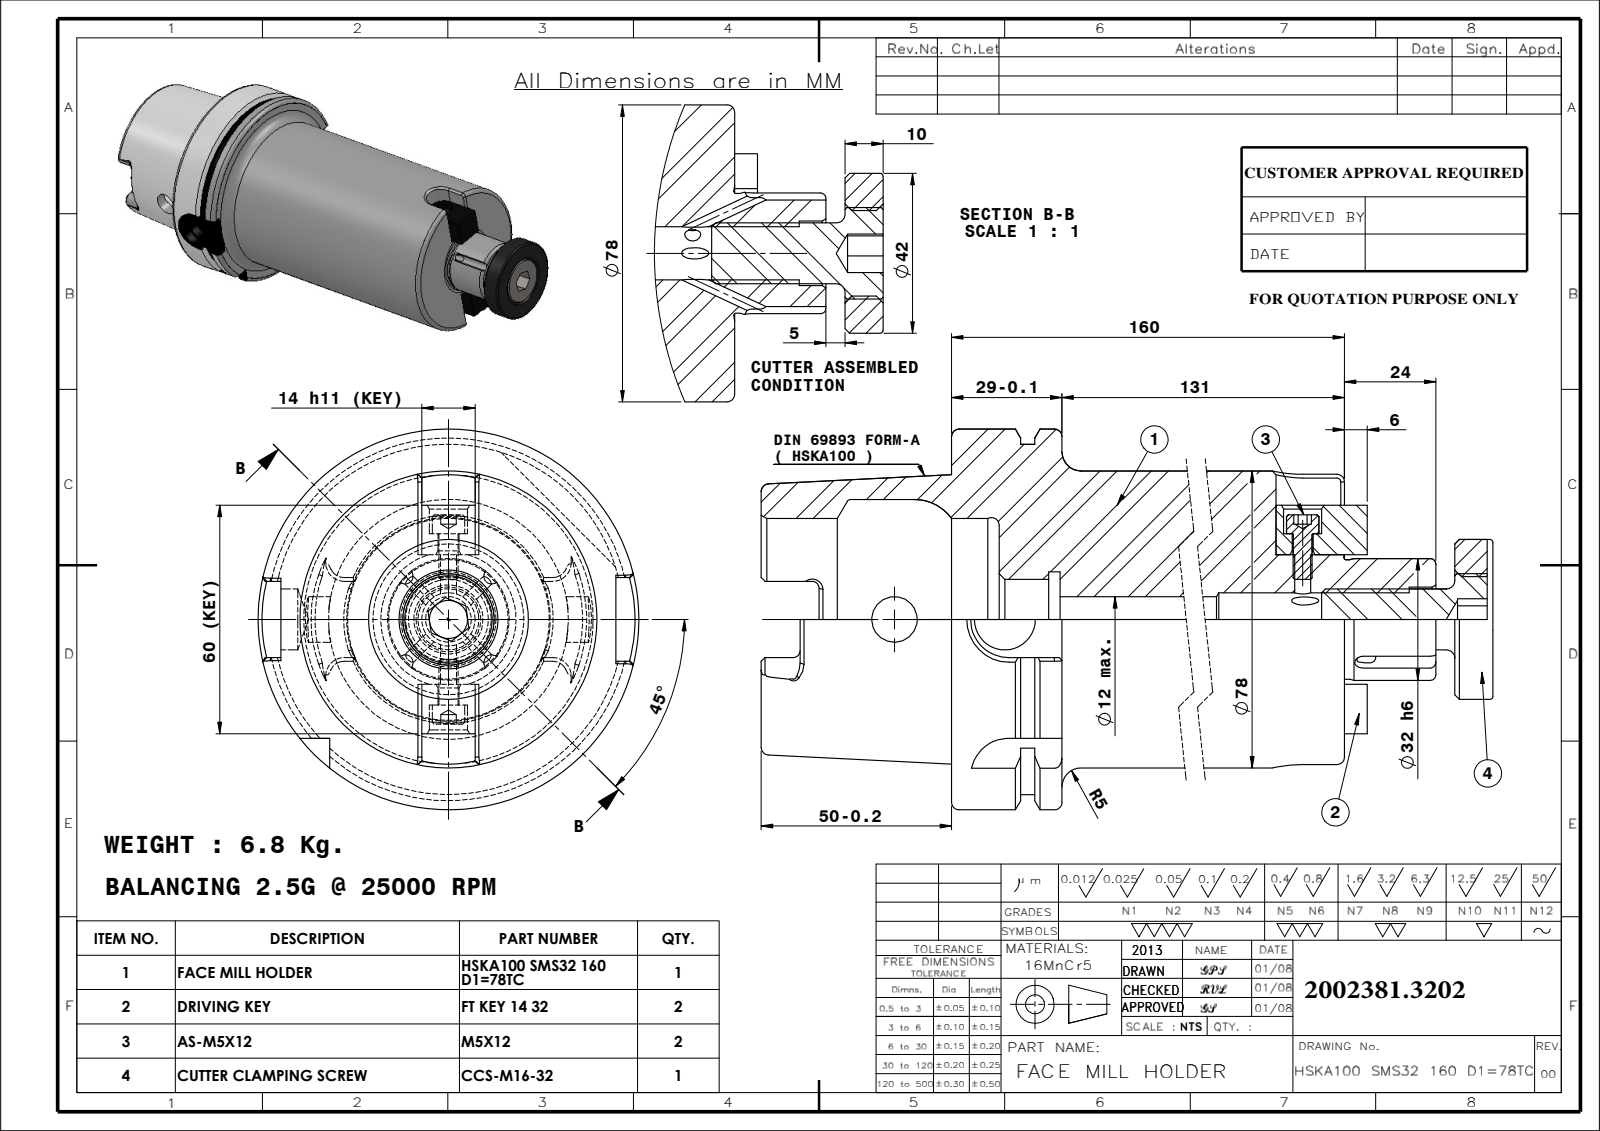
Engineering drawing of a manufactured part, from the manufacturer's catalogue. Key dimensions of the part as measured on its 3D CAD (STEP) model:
Part name (STEP PRODUCT): CCS-M16-32-1; CCS-M16-32; HSKA100 SMS32 160 D1=78TC; FT KEY 14 32 (+2 more)
STEP written by: SolidWorks 2009 (CONFIG_CONTROL_DESIGN)
Units: millimetres
Bodies: 7 solids, 377 faces (137 planar, 98 cylindrical, 142 other)
Overall size (bounding box): 249 × 100 × 100
Volume: 895 616 mm³ · Surface area: 103 414 mm²
Round holes (diameter × count): ⌀3 ×4, ⌀12 ×2, ⌀4.2 ×1, ⌀5.5 ×1, ⌀10 ×1, ⌀14 ×1, ⌀16 ×1, ⌀17 ×1, ⌀21 ×1, ⌀22.5 ×1, ⌀25 ×1, ⌀53 ×1
Round bosses / shafts (diameter × count): ⌀100 ×1, ⌀92 ×1, ⌀78 ×1, ⌀42 ×1, ⌀32 ×1, ⌀31.4 ×1, ⌀24 ×1, ⌀16 ×1
Partial cylindrical surfaces — rounded edges, fillets, slot ends (radius × count): R1.8 ×6, R2 ×4, R4.88 ×4, R10 ×2, R7 ×1, R11 ×1
Main face-to-face distances: 160, 29, 12.5, 147.5, 199, 186.5, 39, 16.5, 131, 170
Hole centre spacings: 29
